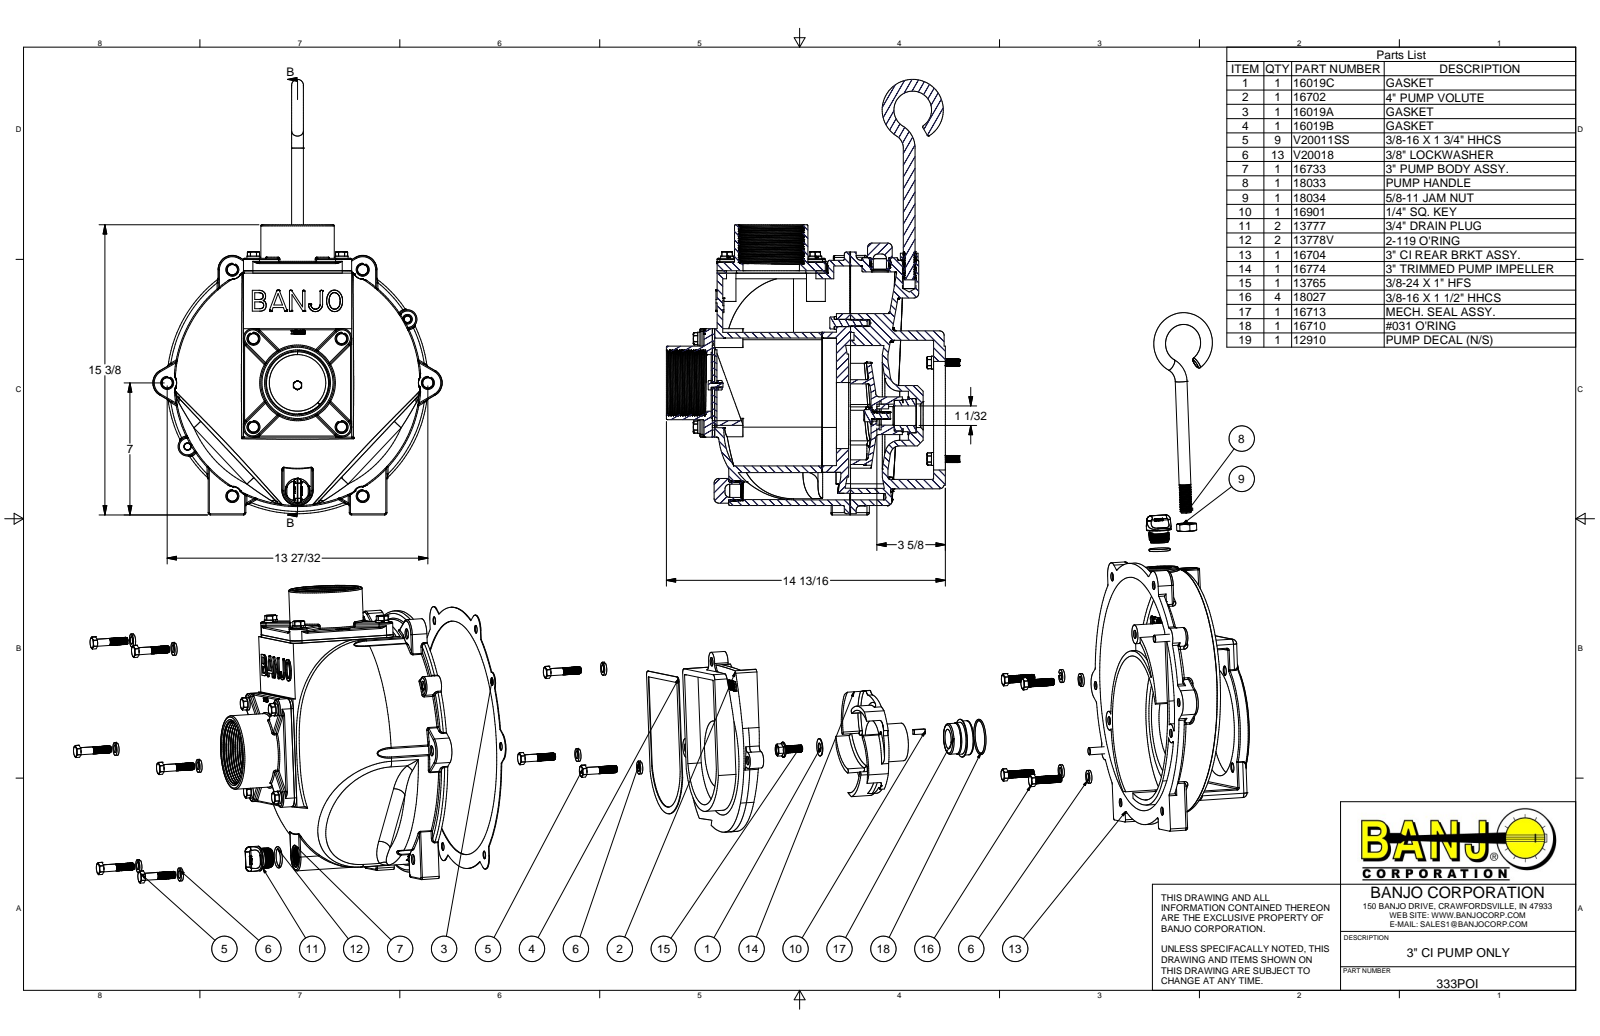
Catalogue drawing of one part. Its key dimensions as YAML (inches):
part_name: "333POI; 16704; 16704X; 16020 (+8 more)"
step_written_by: "Autodesk Inventor 2013 (AUTOMOTIVE_DESIGN)"
units: inches
bodies: {solids: 70, faces: 6774, planar: 1118, cylindrical: 2610, other: 3046}
overall_size: [23.09, 15.585, 15.375]
volume: 404.4
surface_area: 2750
round_holes:
  - {diameter: 0.385, count: 21}
  - {diameter: 0.307, count: 17}
  - {diameter: 0.406, count: 16}
  - {diameter: 0.4, count: 8}
  - {diameter: 0.413, count: 6}
  - {diameter: 0.438, count: 4}
  - {diameter: 0.393, count: 3}
  - {diameter: 0.548, count: 3}
  - {diameter: 0.374, count: 2}
  - {diameter: 0.39, count: 2}
  - {diameter: 0.7, count: 2}
  - {diameter: 1.17, count: 2}
round_bosses_or_shafts:
  - {diameter: 0.324, count: 411}
  - {diameter: 0.375, count: 23}
  - {diameter: 0.687, count: 21}
  - {diameter: 0.212, count: 12}
  - {diameter: 1, count: 10}
  - {diameter: 4.5, count: 2}
  - {diameter: 3.9, count: 2}
  - {diameter: 1.31, count: 2}
partial_cylinders:
  - {radius: 0.06, count: 129}
  - {radius: 0.125, count: 84}
  - {radius: 0.162, count: 42}
  - {radius: 0.25, count: 24}
  - {radius: 0.5, count: 20}
  - {radius: 0.322, count: 12}
  - {radius: 0.75, count: 10}
  - {radius: 0.32, count: 9}
face_to_face_distances: [0.3, 0.031, 7.315, 7.346, 5.05, 0.125, 7.19, 7.222, 0.5, 0.75]
hole_center_spacings: [12.008, 4.685, 6.933, 6.937, 6.928, 12.016, 3.25, 3.313]
